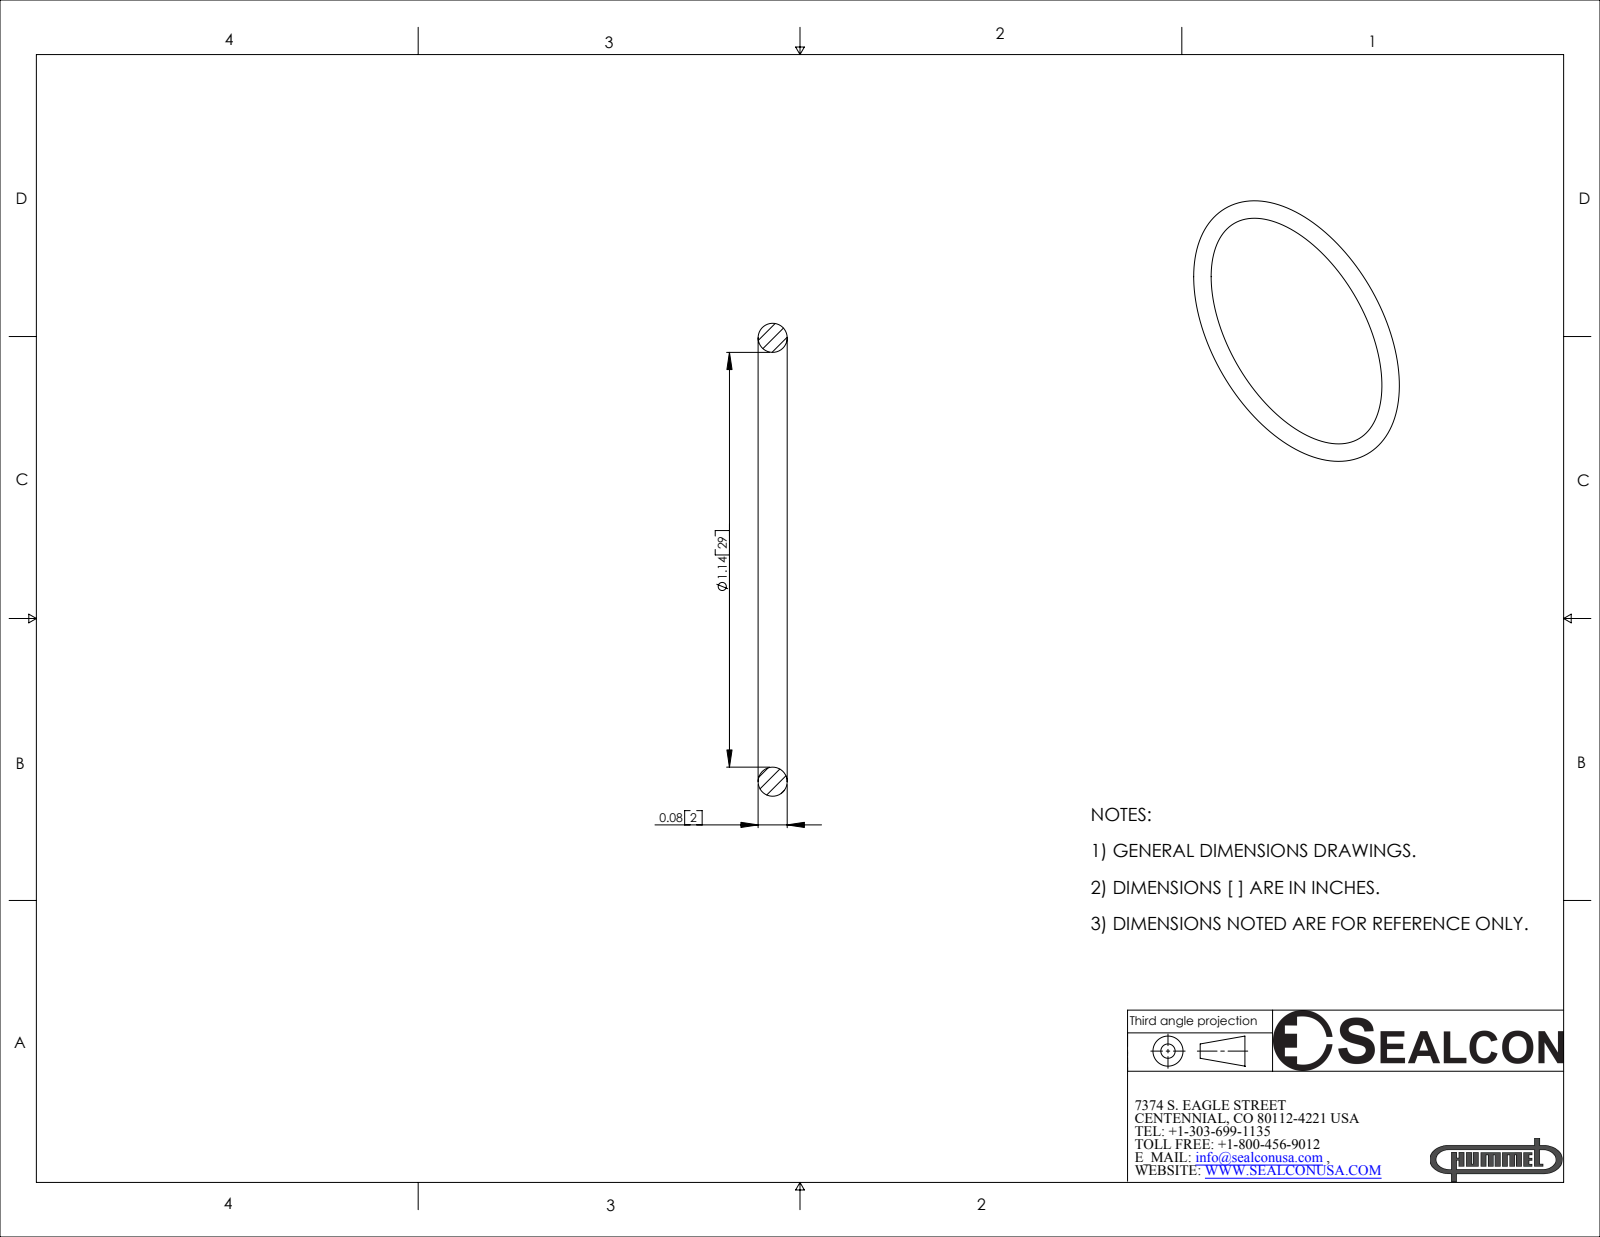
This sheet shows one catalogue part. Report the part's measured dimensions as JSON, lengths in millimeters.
{"part_name": "OM-32-VT", "step_written_by": "SolidWorks 2007 (CONFIG_CONTROL_DESIGN)", "units": "millimeters", "bodies": {"solids": 1, "faces": 4, "planar": 0, "cylindrical": 0, "other": 4}, "overall_size": [33, 33, 2], "volume_mm3": 310, "surface_area_mm2": 621}
